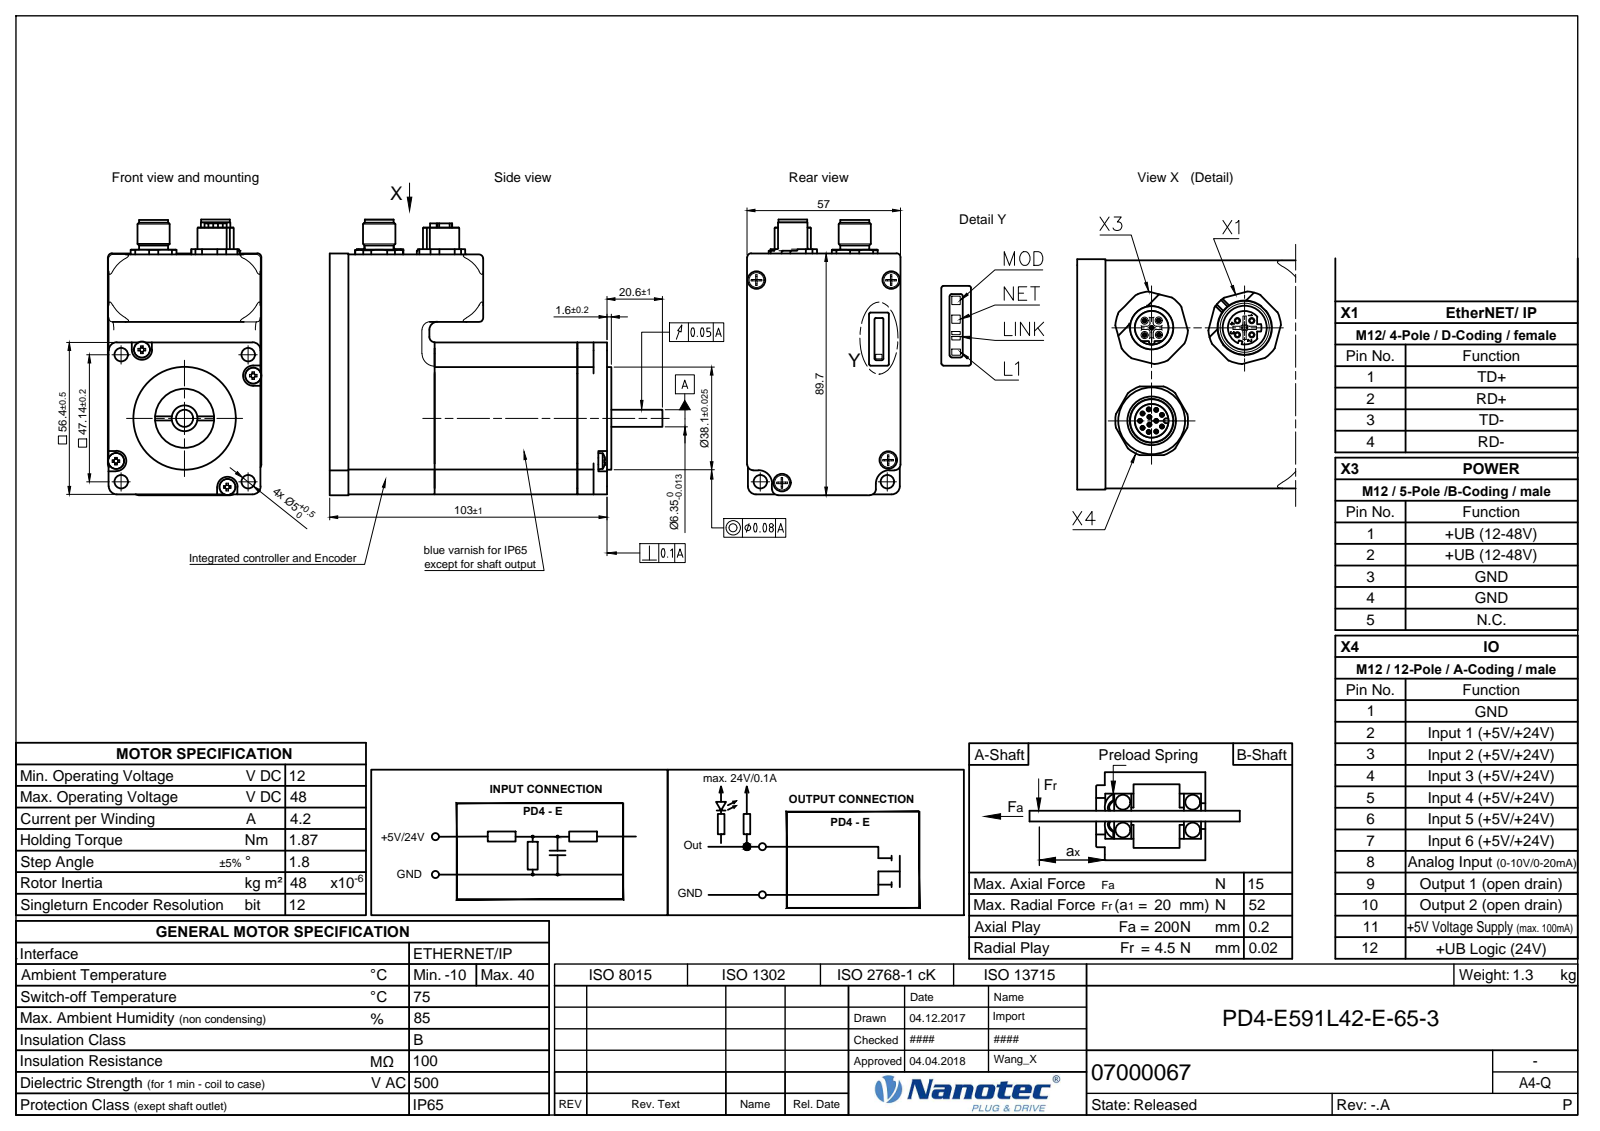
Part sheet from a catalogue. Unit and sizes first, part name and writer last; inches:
Units: inches
Overall size (bounding box): 4.866 × 4.028 × 2.244
Round holes (diameter × count): ⌀0.047 ×12, ⌀0.098 ×6, ⌀0.043 ×5, ⌀0.067 ×4, ⌀0.126 ×4, ⌀0.134 ×4, ⌀0.197 ×4, ⌀0.602 ×3, ⌀0.079 ×2, ⌀0.079 ×2, ⌀0.097 ×2, ⌀0.327 ×1
Round bosses / shafts (diameter × count): ⌀0.043 ×12, ⌀0.025 ×12, ⌀0.051 ×9, ⌀0.118 ×8, ⌀0.039 ×5, ⌀0.217 ×4, ⌀0.108 ×4, ⌀0.106 ×4
Partial cylindrical surfaces — rounded edges, fillets, slot ends (radius × count): R0.079 ×44, R0.008 ×20, R0.02 ×16, R0.012 ×15, R0.004 ×12, R0.087 ×12, R0.006 ×10, R0.059 ×10
Main face-to-face distances: 2.22, 0.098, 3.622, 0.13, 3.492, 1.063, 2.122, 2.52, 1.181, 3.504
Hole centre spacings: 0.139, 0.114, 0.098, 0.074, 0.19, 0.073, 0.197, 0.221
Volume: 15.23 in³ · Surface area: 131.2 in²
Bodies: 16 solids, 1300 faces (609 planar, 419 cylindrical, 272 other)
Part name (STEP PRODUCT): PD4-E591L42-E-65-3
STEP written by: Autodesk Inventor 2017 (AUTOMOTIVE_DESIGN)
